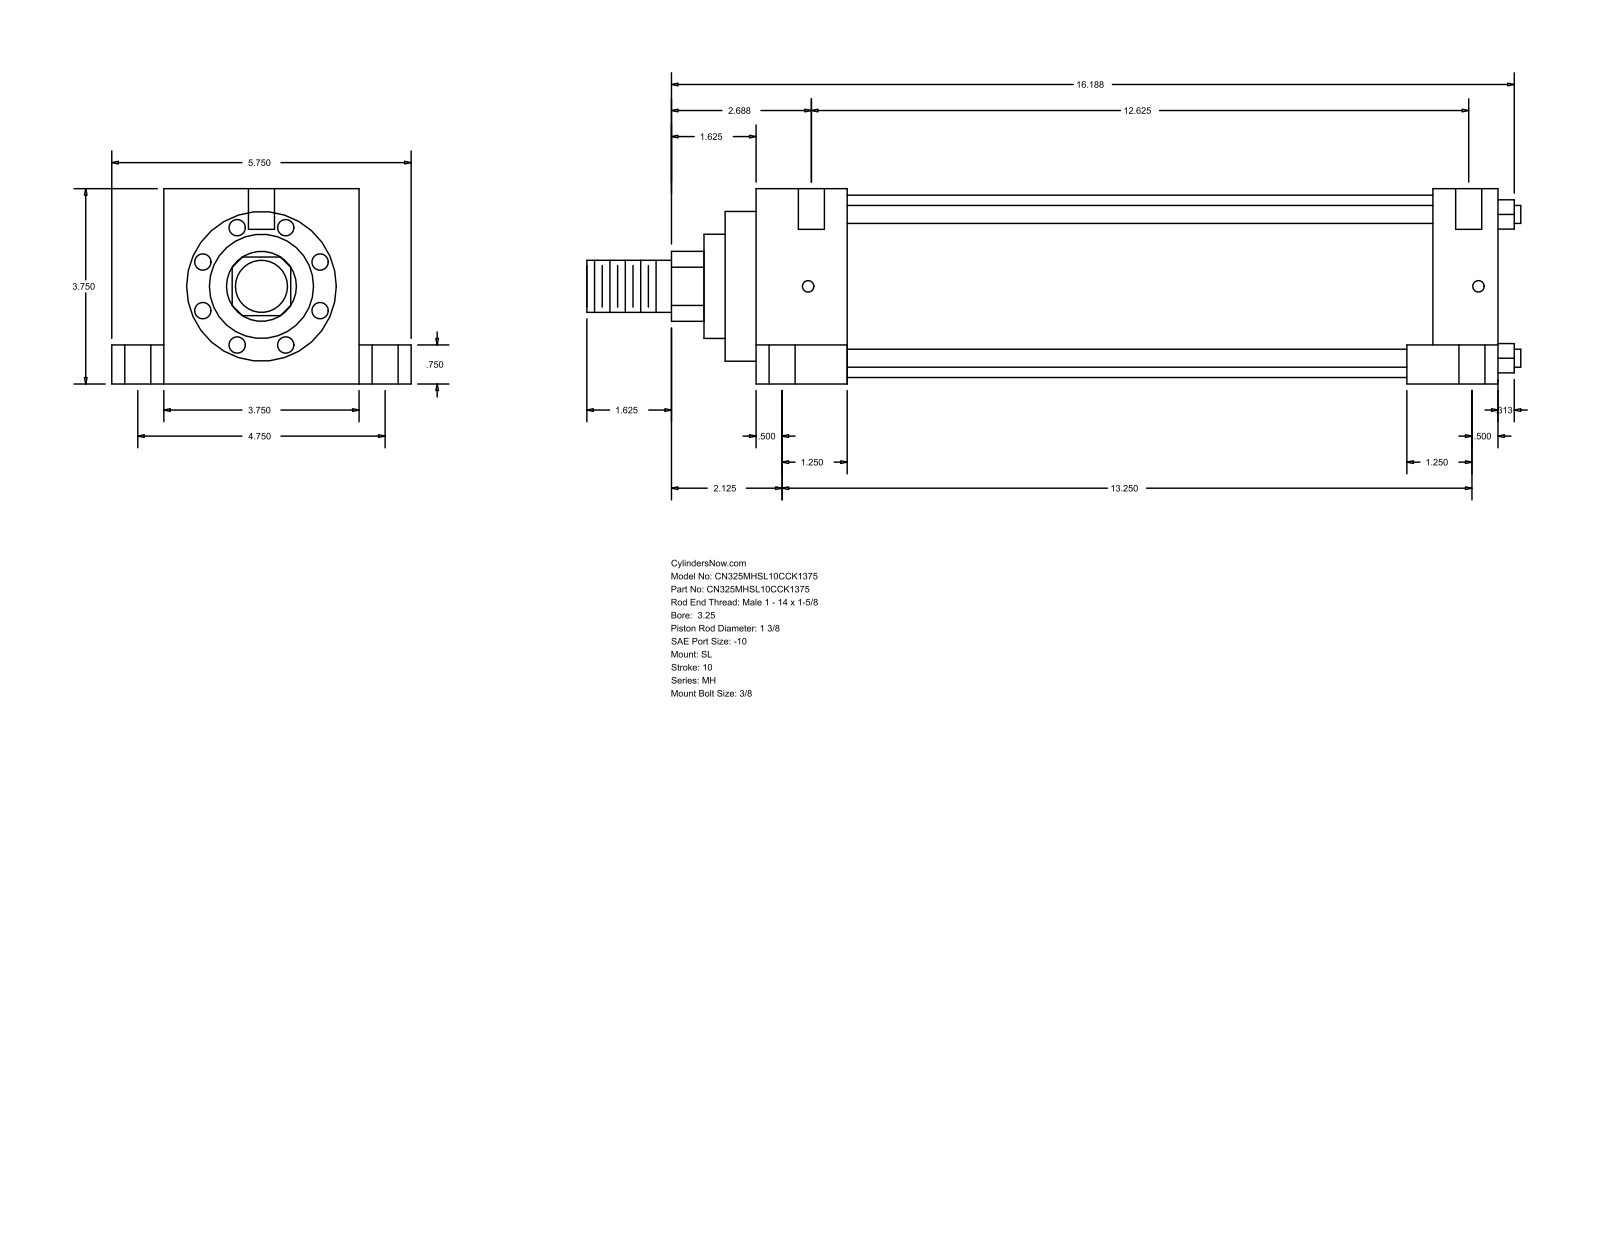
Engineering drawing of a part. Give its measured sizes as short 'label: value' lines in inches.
name: MH_SL__0325_1.375
written by: GSSL Pune (CONFIG_CONTROL_DESIGN)
unit: in
bodies: 0 solids, 110 faces (77 planar, 33 cylindrical, 0 other)
size: 17.937 × 5.75 × 3.75
holes: 6× ⌀0.5, 4× ⌀0.219, 4× ⌀0.75
bosses: 4× ⌀0.345, 1× ⌀3.5, 1× ⌀2.875, 1× ⌀2, 1× ⌀1.375, 1× ⌀1
rounds: 1× R0.672
face distances: 3.75, 14.25, 1.75, 12.5, 1, 4.75, 0.75, 3, 13, 11.25
hole spacings: 2.376, 2.378, 2.427, 2.441, 4.75, 12.875, 12.908, 12.969
